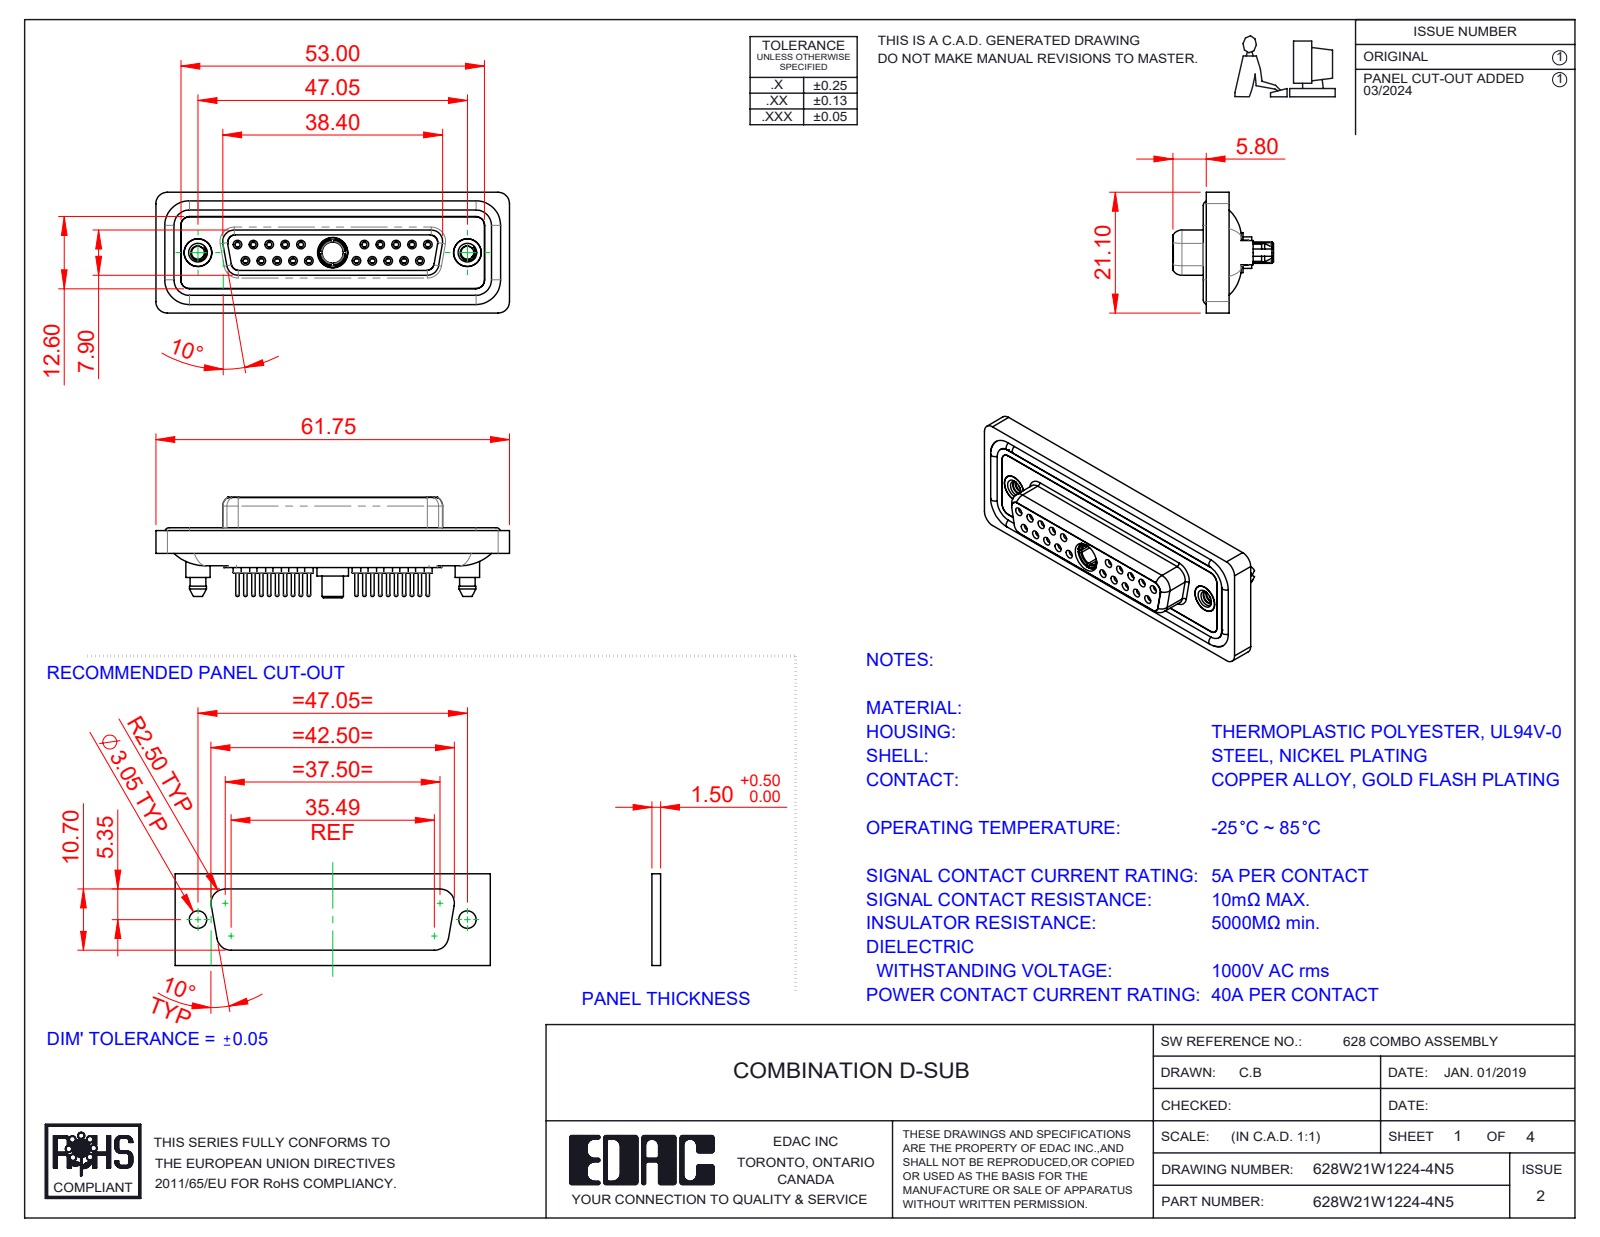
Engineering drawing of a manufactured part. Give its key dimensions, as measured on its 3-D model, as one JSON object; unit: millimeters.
{"part_name": "628Combo Shell Front_25 Contacts; 628Combo Contact Row 1_24; Power Socket_40A S; 628Combo Contact Row 2_24 (+5 more)", "step_written_by": "SolidWorks 2023 (CONFIG_CONTROL_DESIGN)", "units": "millimeters", "bodies": {"solids": 29, "faces": 1610, "planar": 450, "cylindrical": 623, "other": 537}, "overall_size": [61.75, 21.1, 17.55], "volume_mm3": 8526, "surface_area_mm2": 14346, "round_holes": [[0.9, 20], [1.1, 20], [1.5, 20], [2, 20], [1.6, 10], [1.7, 10], [4.85, 3], [2.26, 2], [4, 2], [4.05, 2], [5, 2], [3.7, 1]], "round_bosses_or_shafts": [[2.2, 20], [0.6, 20], [1.6, 14], [5.4, 2], [4.95, 2], [4.8, 2], [4.25, 2], [5.5, 1]], "partial_cylinders_radius": [[1.5, 24], [2, 18], [1.6, 10], [1.35, 8], [0.25, 4], [0.5, 4], [0.6, 4], [0.65, 4]], "face_to_face_distances": [0.4, 1.8, 7.45, 6.6, 5.65, 1.6, 0.5, 7.05, 2.9, 1.1], "hole_center_spacings": [3.16, 2.77, 5.54, 5.03, 8.31, 7.48, 16.62, 19.39]}
